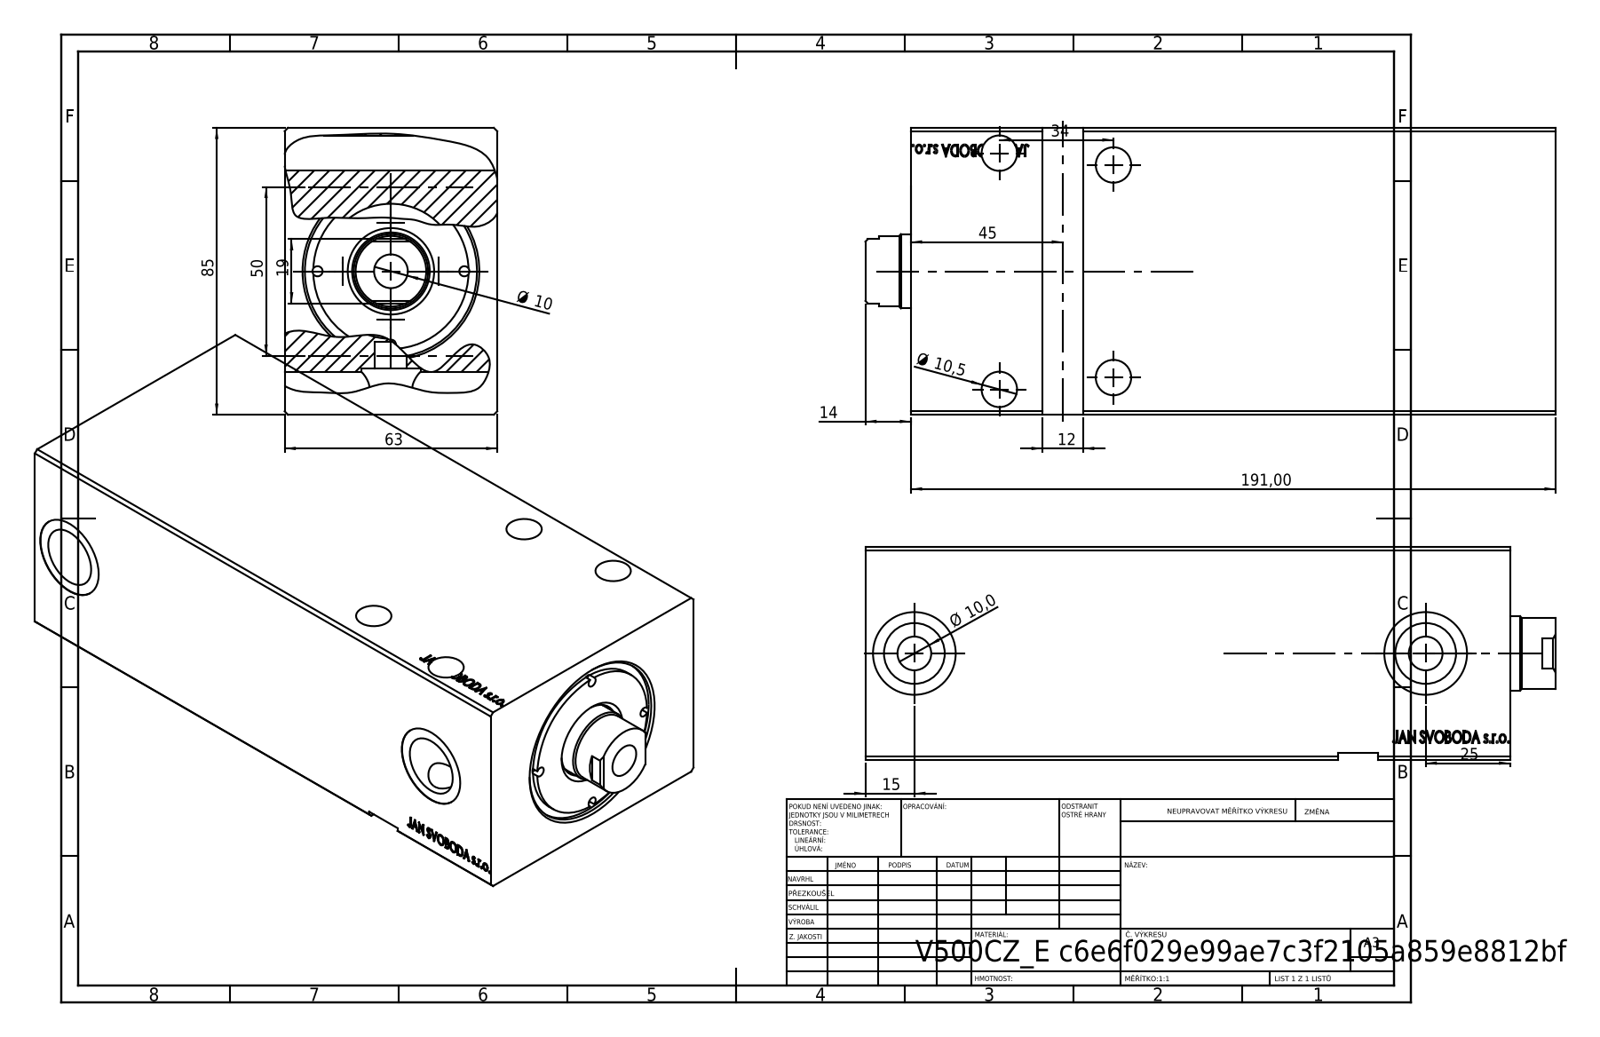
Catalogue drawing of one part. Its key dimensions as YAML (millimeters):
part_name: "V500CZ_E; V500CZ_VC_vysunovaci_E; V500CZ_VCP_E"
step_written_by: "SolidWorks 2019 (CONFIG_CONTROL_DESIGN)"
units: millimeters
bodies: {solids: 3, faces: 779, planar: 365, cylindrical: 54, other: 360}
overall_size: [204.5, 85, 63]
volume: 891486
surface_area: 118168
round_holes:
  - {diameter: 3, count: 4}
  - {diameter: 10.5, count: 4}
  - {diameter: 10, count: 3}
  - {diameter: 18, count: 2}
  - {diameter: 24.5, count: 2}
  - {diameter: 22, count: 1}
  - {diameter: 23, count: 1}
  - {diameter: 36, count: 1}
  - {diameter: 40, count: 1}
  - {diameter: 51, count: 1}
round_bosses_or_shafts:
  - {diameter: 46, count: 1}
  - {diameter: 20.92, count: 1}
face_to_face_distances: [63, 85, 191, 155, 36, 61, 11.8, 143.2, 179.2, 1.8]
hole_center_spacings: [21.75, 30.76, 34, 43.5, 74.61, 63, 70, 151.5]
